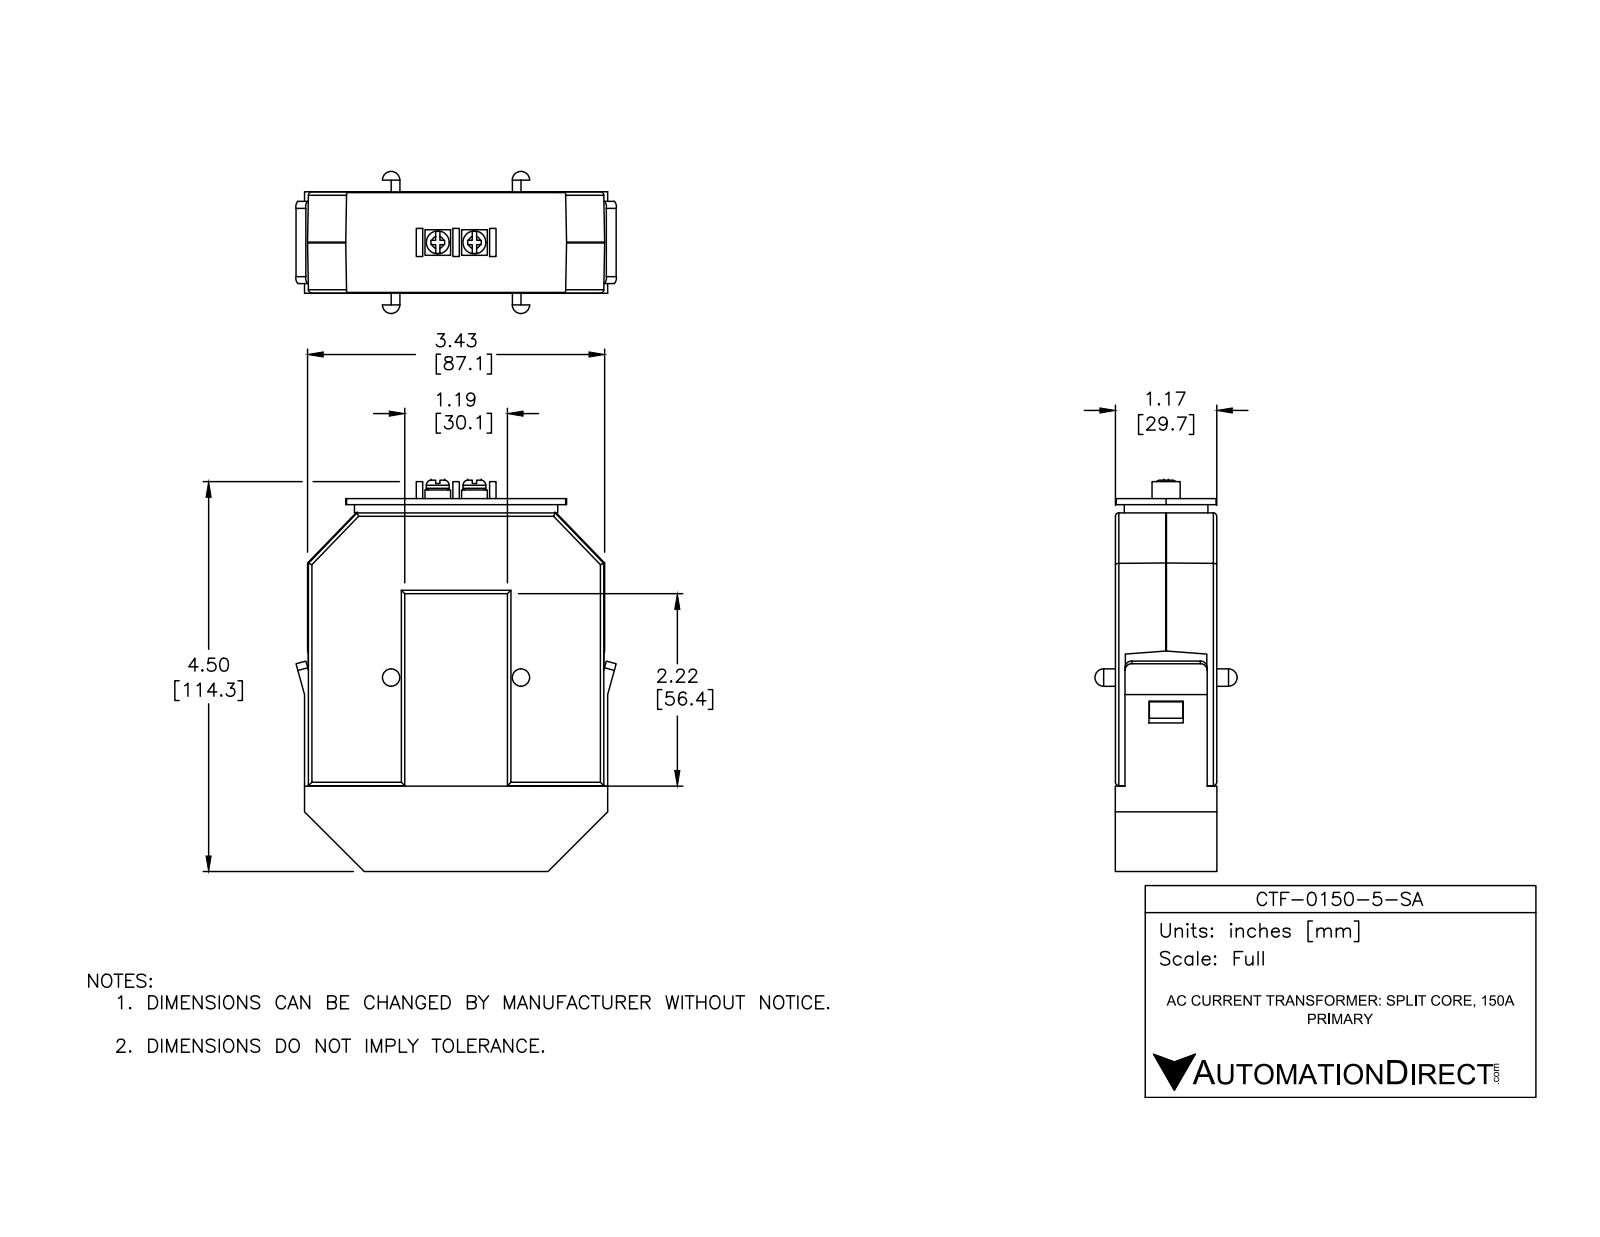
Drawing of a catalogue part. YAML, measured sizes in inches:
part_name: "CTF-0150-5-SA"
step_written_by: "SolidWorks 2016 (AUTOMOTIVE_DESIGN)"
units: inches
bodies: {solids: 8, faces: 210, planar: 160, cylindrical: 34, other: 16}
overall_size: [4.517, 3.696, 1.642]
volume: 13.27
surface_area: 62.61
round_bosses_or_shafts:
  - {diameter: 0.264, count: 2}
partial_cylinders:
  - {radius: 0.04, count: 18}
  - {radius: 0.08, count: 4}
  - {radius: 0.1, count: 2}
face_to_face_distances: [1.169, 1.17, 2.22, 3.319, 1.172, 0.118, 1.157, 2.342, 0.986, 4.305]
